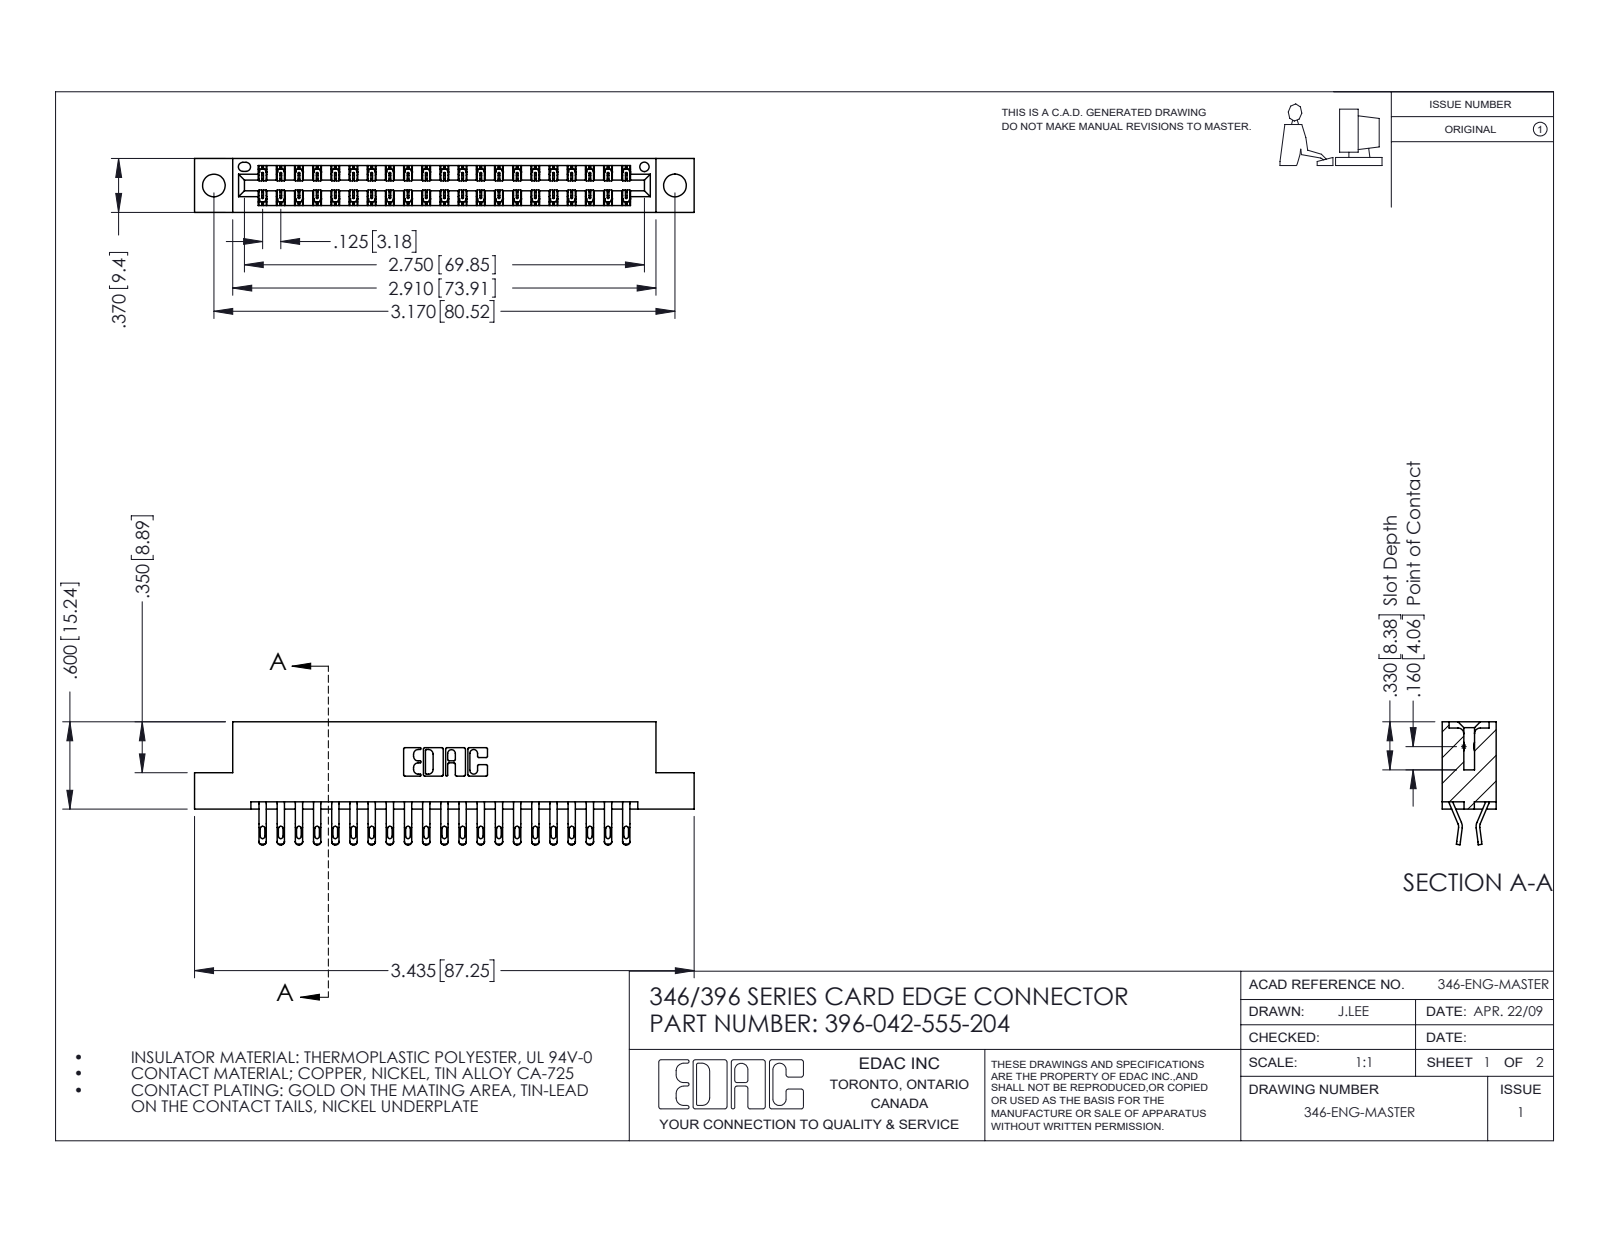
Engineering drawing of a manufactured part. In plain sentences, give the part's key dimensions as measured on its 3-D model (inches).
The part is named "396-042-555-204; 345-292-001_555 Tail; 346 Part_Flush Mounting Lugs - 0.156 Dia-TH". Its 3-D file was written by "SolidWorks 2016 (CONFIG_CONTROL_DESIGN)". It is 43 solids with 2558 faces: 1462 planar, 1096 cylindrical and 0 other. Overall it measures 3.435 by 0.845 by 0.37 inches. Its volume is 0.511 cubic inches and its surface area 17.72 square inches. Round holes: 2 of diameter 0.156, 1 of diameter 0.064. Partial cylindrical surfaces (rounded edges, fillets, slot ends): 84 of radius 0.016, 84 of radius 0.02, 63 of radius 0.006, 22 of radius 0.01, 6 of radius 0.007, 6 of radius 0.031, 3 of radius 0.026, 2 of radius 0.01. The main face-to-face distances are 0.048, 0.322, 0.25, 0.37, 0.025, 0.072, 0.298, 0.275, 0.148, 0.222. The hole center spacings are 0.246, 2.963, 3.17.
